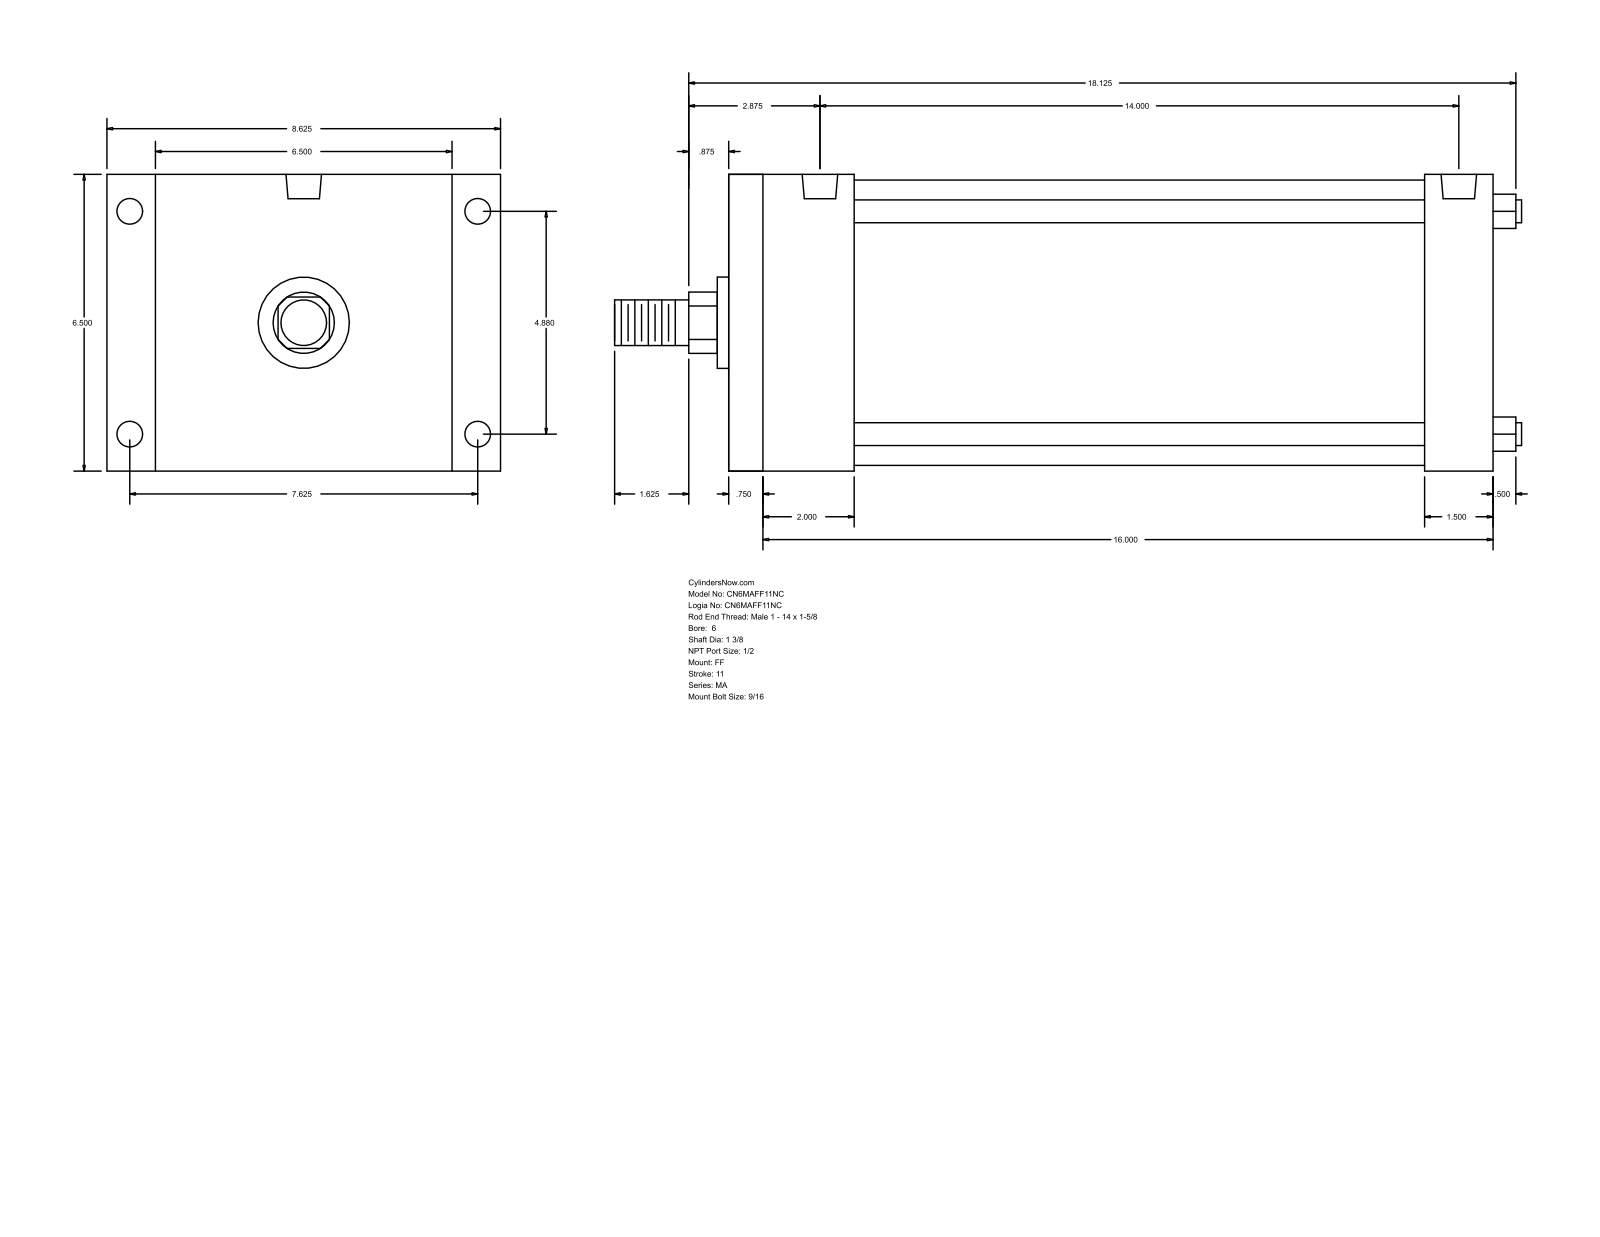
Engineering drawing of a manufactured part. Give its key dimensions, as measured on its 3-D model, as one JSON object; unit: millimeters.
{"part_name": "MA_FF__0600_1.375", "step_written_by": "GSSL Pune (CONFIG_CONTROL_DESIGN)", "units": "millimeters", "bodies": {"solids": 0, "faces": 92, "planar": 64, "cylindrical": 28, "other": 0}, "overall_size": [504.82, 219.07, 165.1], "round_holes": [[14.29, 4], [17.46, 4], [19.77, 2]], "round_bosses_or_shafts": [[12.7, 4], [158.75, 1], [50.8, 1], [34.92, 1], [25.4, 1]], "partial_cylinders_radius": [[17.06, 1]], "face_to_face_distances": [165.1, 425.45, 15.87, 409.58, 66.67, 50.8, 358.78, 387.34, 371.47, 320.67], "hole_center_spacings": [123.96, 193.68, 229.95, 358.77, 3.18, 355.59]}
